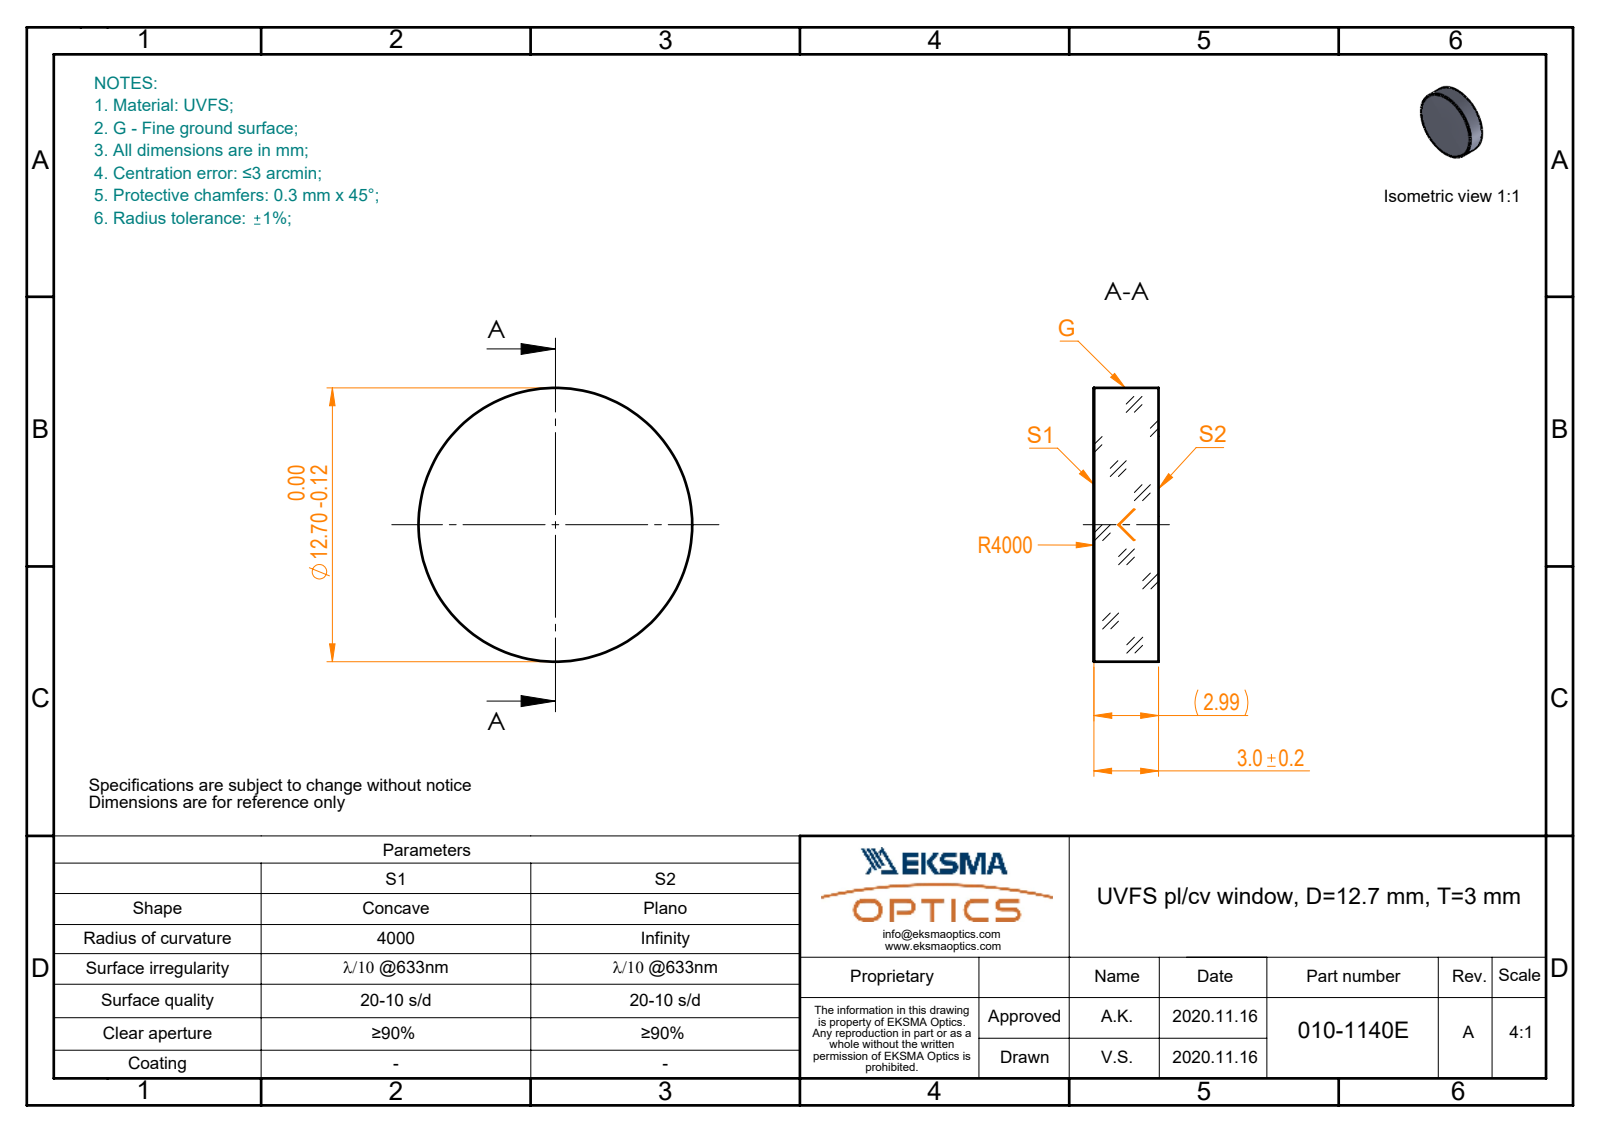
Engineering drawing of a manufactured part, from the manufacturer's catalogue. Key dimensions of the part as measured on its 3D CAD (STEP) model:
Part name (STEP PRODUCT): 010-1140E_UVFS_PCV_window
STEP written by: SolidWorks 2019 (CONFIG_CONTROL_DESIGN)
Units: millimetres
Bodies: 1 solid, 5 faces (1 planar, 2 cylindrical, 2 other)
Overall size (bounding box): 12.7 × 12.7 × 3
Volume: 380 mm³ · Surface area: 373 mm²
Round bosses / shafts (diameter × count): ⌀12.7 ×1
